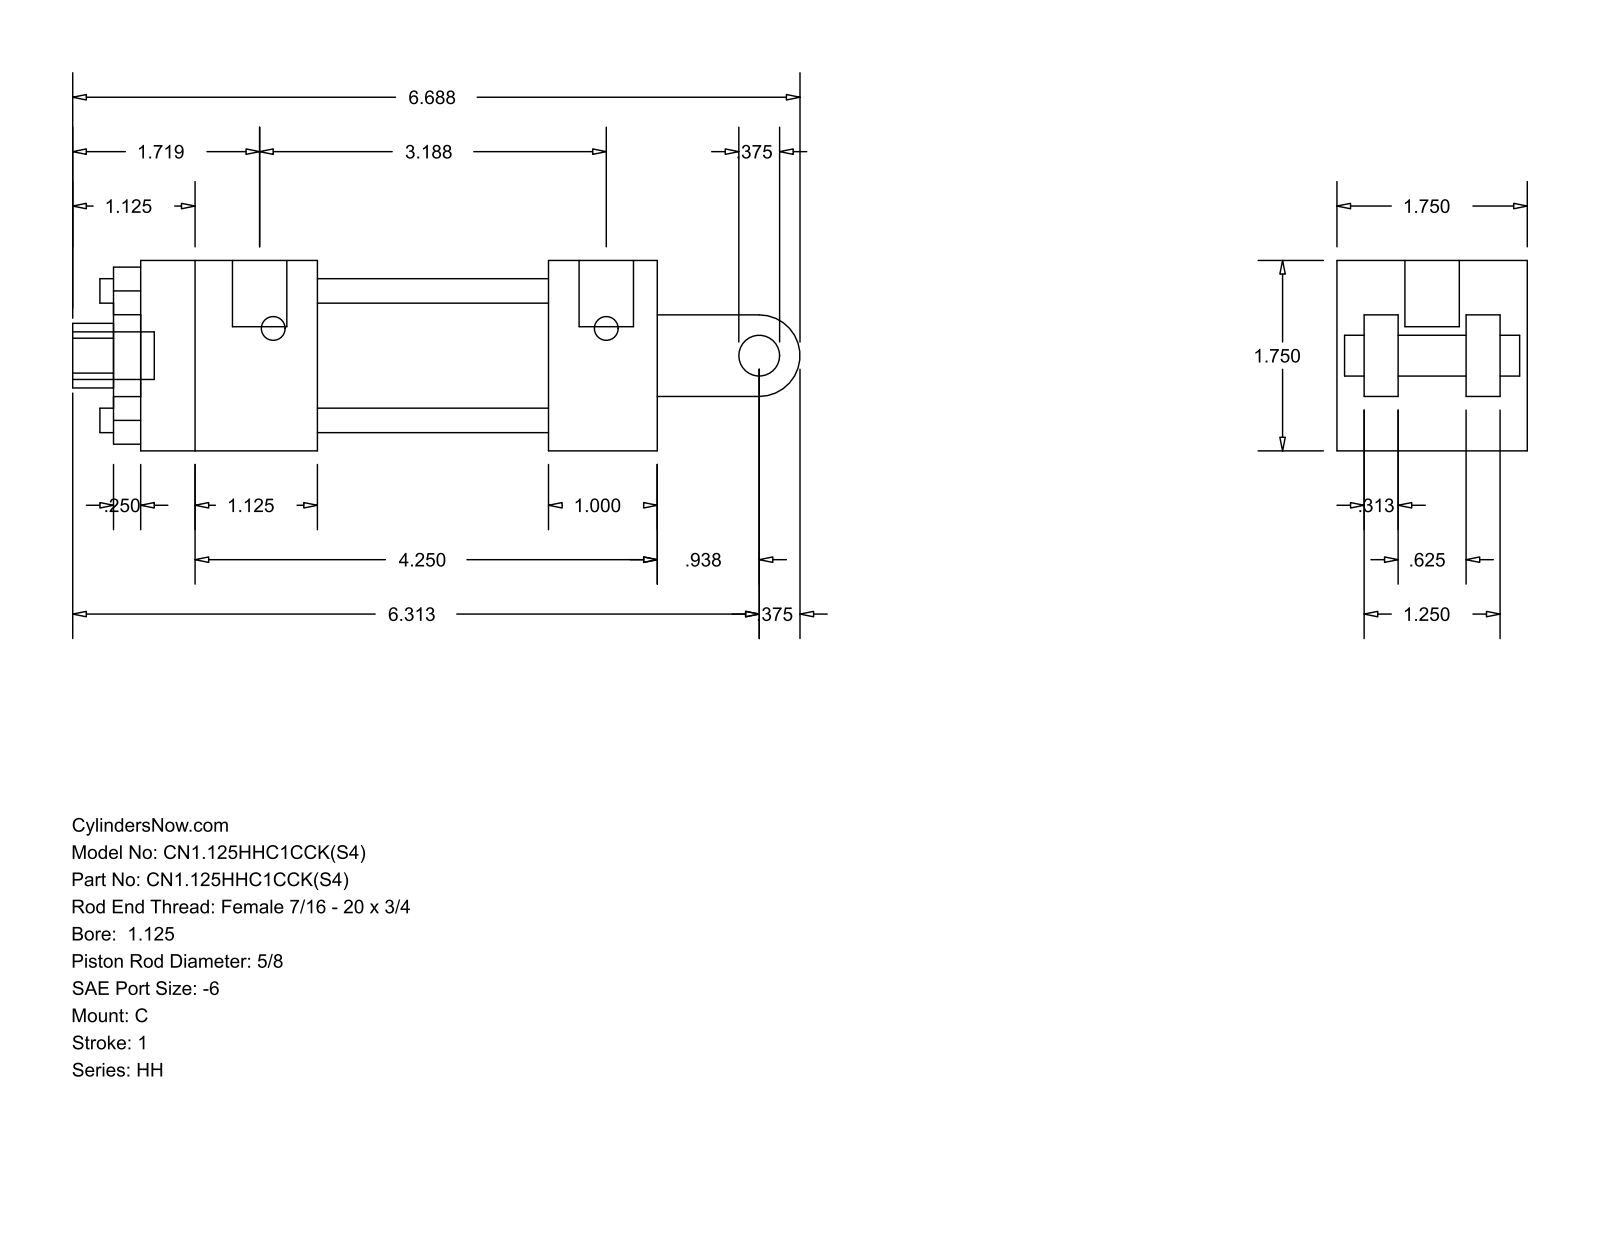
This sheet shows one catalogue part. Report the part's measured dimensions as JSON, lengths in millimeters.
{"part_name": "HH_C__0112_0.625", "step_written_by": "GSSL Pune (CONFIG_CONTROL_DESIGN)", "units": "millimeters", "bodies": {"solids": 0, "faces": 99, "planar": 70, "cylindrical": 29, "other": 0}, "overall_size": [169.86, 44.45, 44.45], "round_holes": [[5.71, 4], [5.56, 2], [12.7, 1], [15.88, 1], [28.57, 1], [34.92, 1]], "round_bosses_or_shafts": [[5.56, 2], [12.7, 1], [11.11, 1], [9.53, 1]], "partial_cylinders_radius": [[7.54, 1], [9.53, 1]], "face_to_face_distances": [44.46, 6.35, 31.76, 14.29, 12.7, 30.17, 38.11, 7.94, 23.82, 41.27], "hole_center_spacings": [21.37, 30.22, 42.74]}
